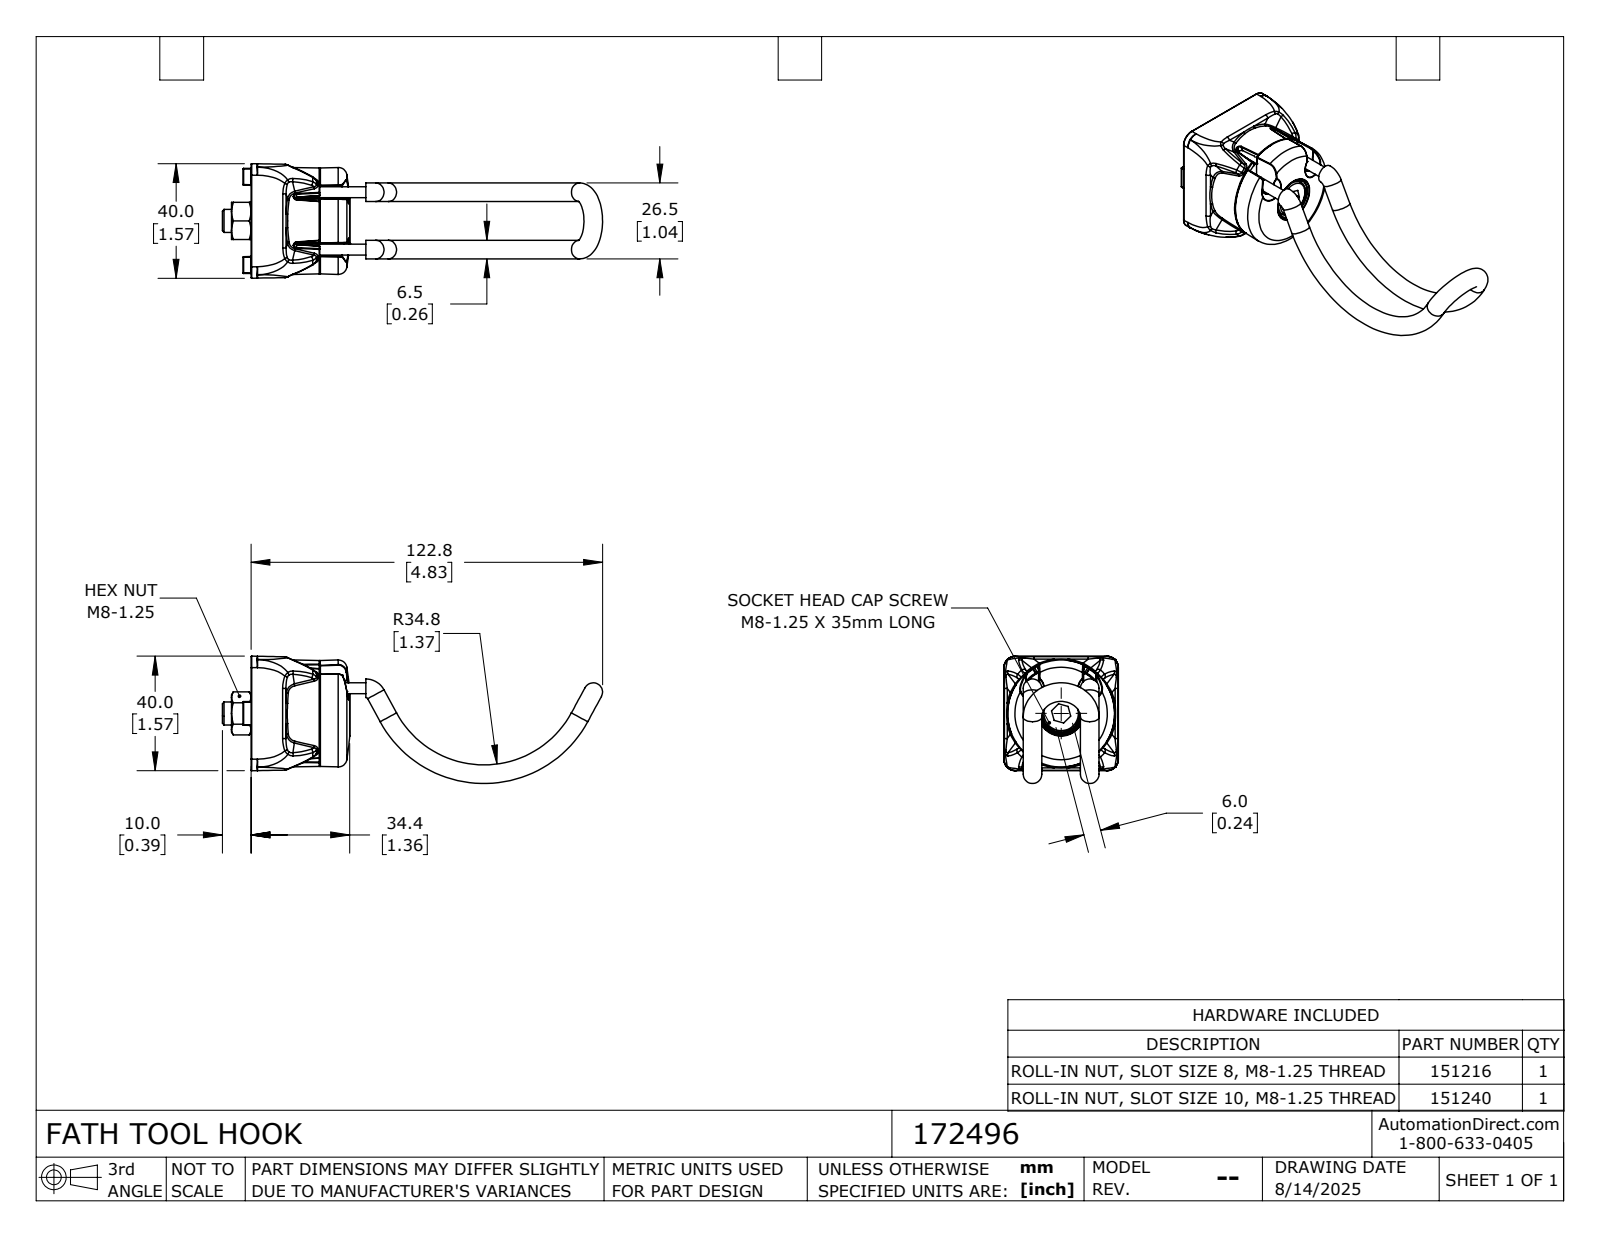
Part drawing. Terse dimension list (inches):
name: 172496
written by: SolidWorks 2024 (CONFIG_CONTROL_DESIGN)
unit: in
bodies: 7 solids, 1249 faces (224 planar, 300 cylindrical, 725 other)
size: 5.227 × 1.75 × 1.575
volume: 2.823 in³; area: 38.4 in²
holes: 1× ⌀0.268, 1× ⌀0.315, 1× ⌀0.512
bosses: 6× ⌀0.15, 2× ⌀0.256, 1× ⌀0.512
rounds: 142× R0.008, 22× R0.02, 8× R0.039, 8× R0.157, 4× R0.047, 2× R0.085, 1× R0.65
face distances: 0.531, 1.213, 0.315, 0.236, 0.524, 0.421, 0.669, 0.945, 0.413, 0.362
